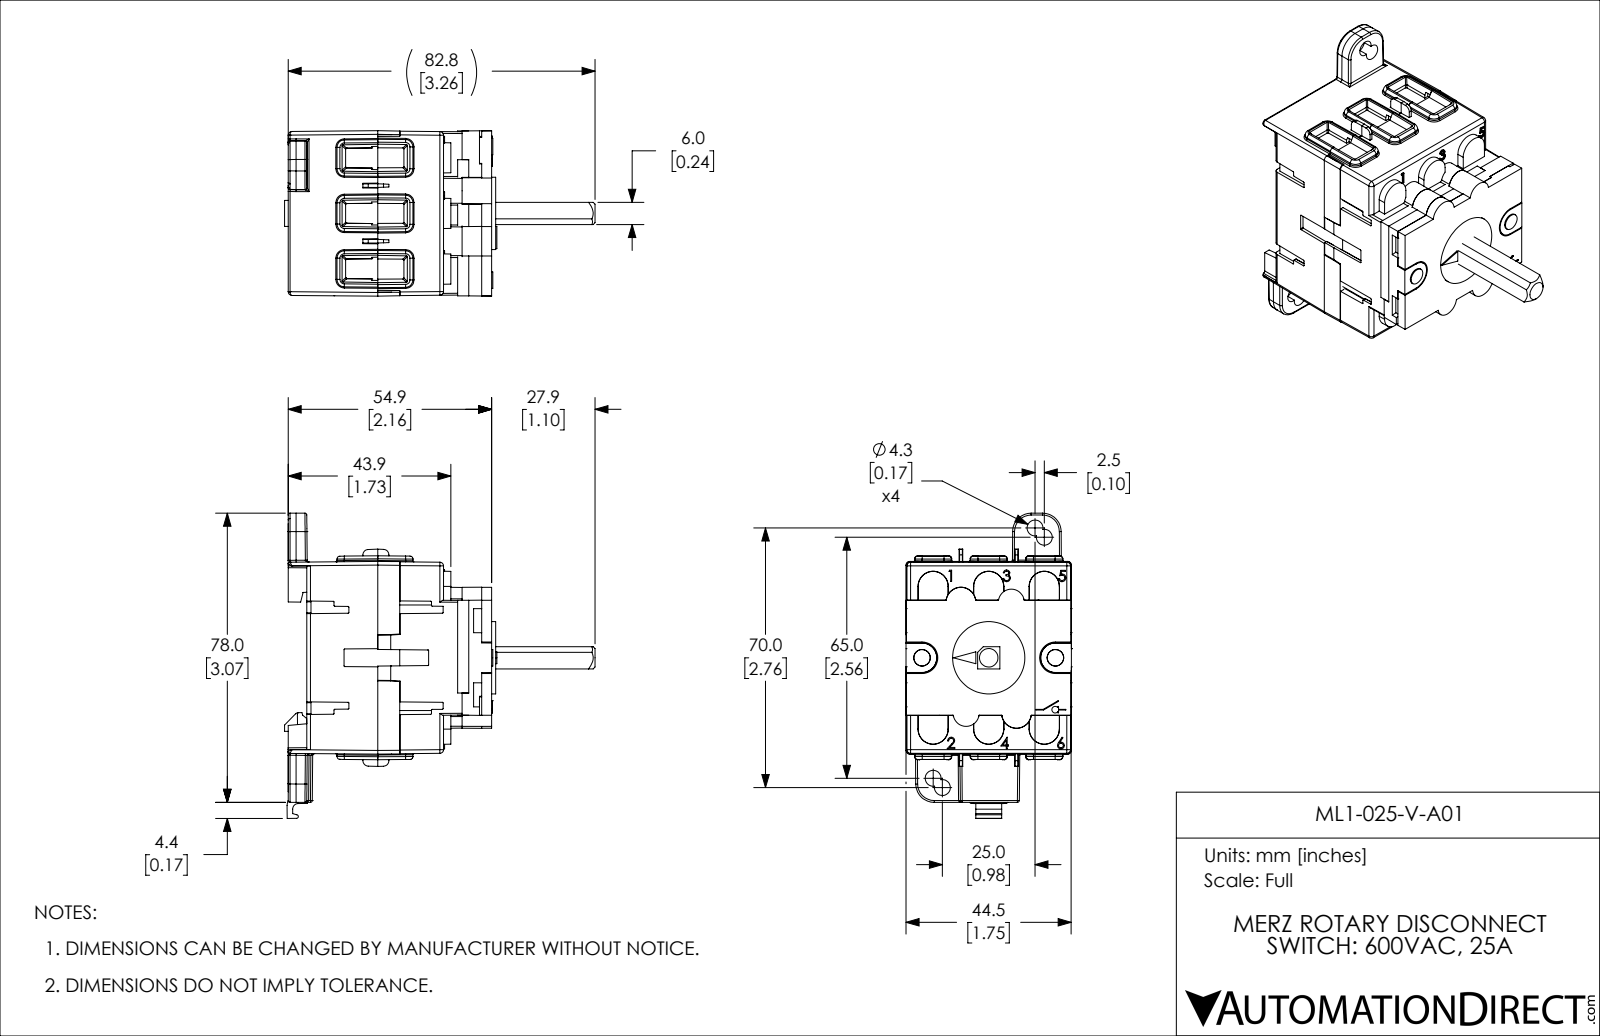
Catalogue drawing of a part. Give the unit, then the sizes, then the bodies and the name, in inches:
Units: inches
Overall size (bounding box): 3.299 × 3.242 × 1.757
Round holes (diameter × count): ⌀0.169 ×4, ⌀0.315 ×1
Round bosses / shafts (diameter × count): ⌀0.276 ×2, ⌀0.768 ×1, ⌀0.646 ×1, ⌀0.472 ×1, ⌀0.335 ×1, ⌀0.315 ×1, ⌀0.118 ×1
Partial cylindrical surfaces — rounded edges, fillets, slot ends (radius × count): R0.008 ×75, R0.012 ×62, R0.02 ×47, R0.039 ×29, R0.031 ×28, R0.011 ×12, R0.079 ×12, R0.197 ×6
Main face-to-face distances: 0.234, 1.104, 0.87, 1.65, 0.988, 0.754, 1.858, 0.209, 0.896, 0.661
Hole centre spacings: 0.139, 2.87, 1.113, 1.122, 1.893, 1.978, 2.819, 2.926
Volume: 7.577 in³ · Surface area: 54.26 in²
Bodies: 7 solids, 1402 faces (776 planar, 412 cylindrical, 214 other)
Part name (STEP PRODUCT): ML1-025-V-A01
STEP written by: SolidWorks 2019 (AUTOMOTIVE_DESIGN)
